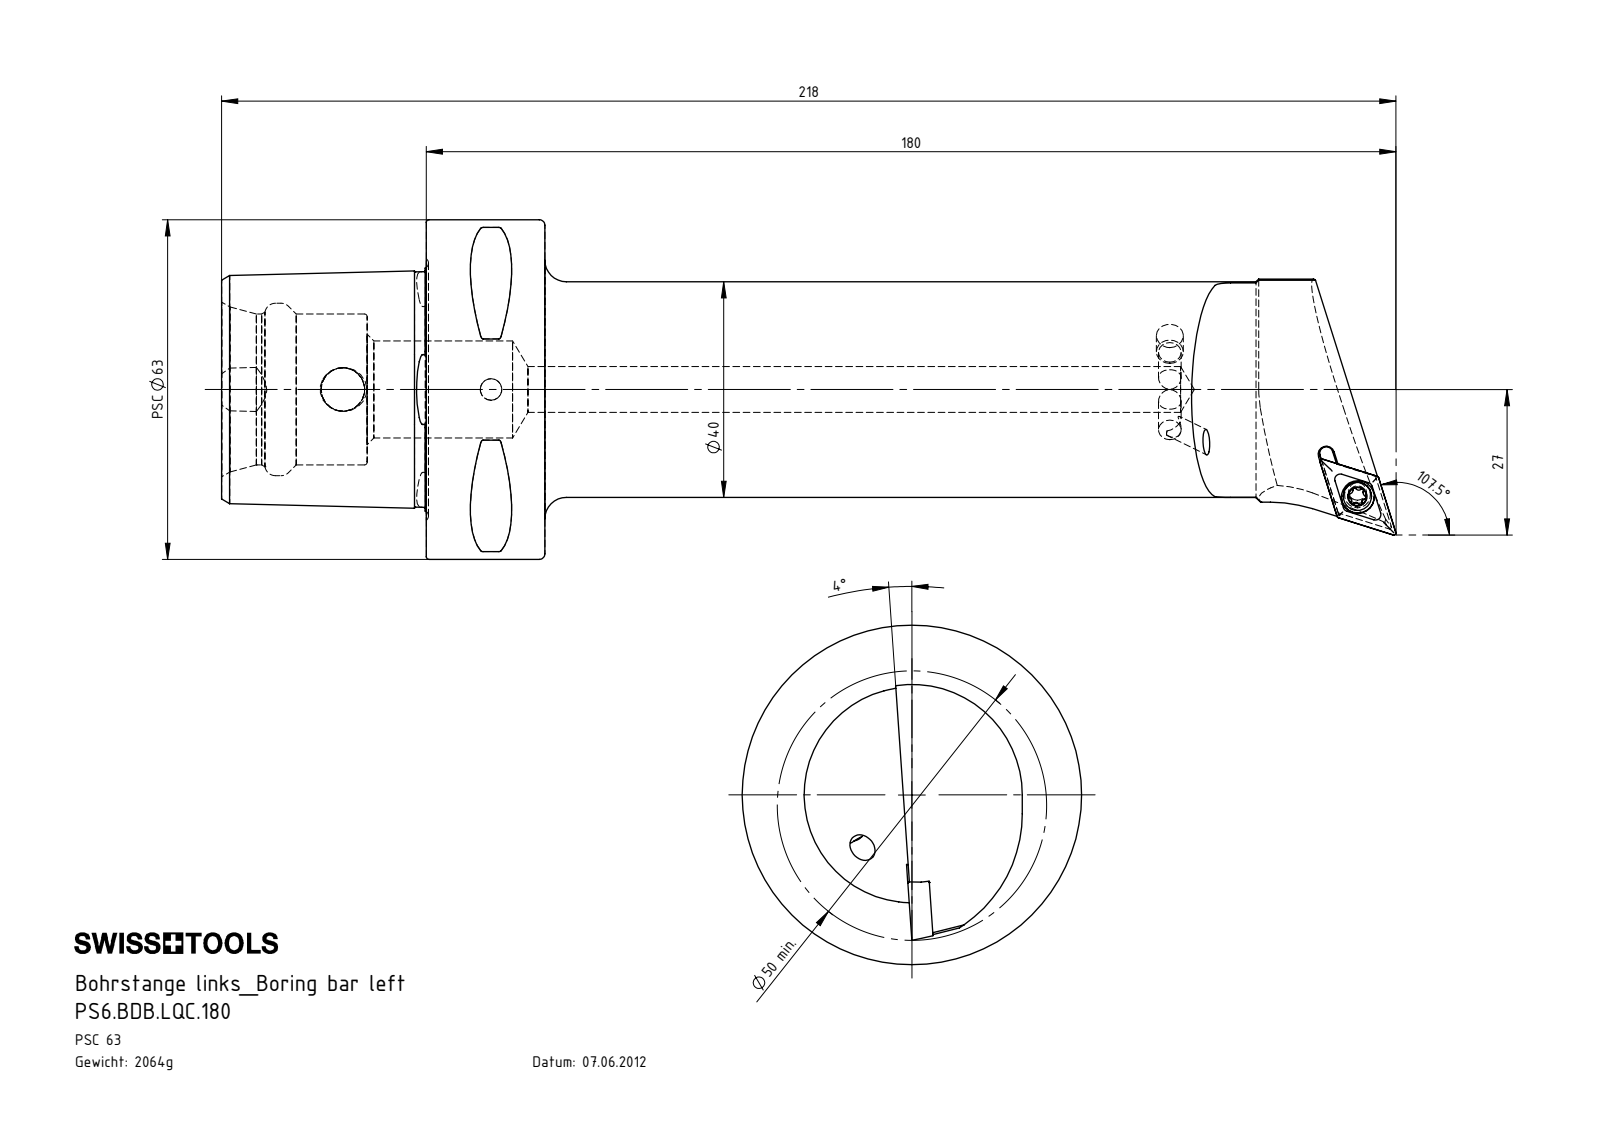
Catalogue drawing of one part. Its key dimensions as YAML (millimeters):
part_name: "PS6-BDB.LQC.180; KVT_MB_600_050; WCB-ER2.001.009_A; DCMT11T304 (+1 more)"
step_written_by: "SolidWorks 2012 (CONFIG_CONTROL_DESIGN)"
units: millimeters
bodies: {solids: 5, faces: 287, planar: 53, cylindrical: 76, other: 158}
overall_size: [218, 63, 63]
volume: 262771
surface_area: 42631
round_holes:
  - {diameter: 4, count: 2}
  - {diameter: 4.2, count: 2}
  - {diameter: 3.3, count: 1}
  - {diameter: 4.4, count: 1}
  - {diameter: 6.1, count: 1}
  - {diameter: 8.1, count: 1}
  - {diameter: 8.5, count: 1}
  - {diameter: 18, count: 1}
  - {diameter: 28, count: 1}
  - {diameter: 32, count: 1}
round_bosses_or_shafts:
  - {diameter: 63, count: 1}
  - {diameter: 40, count: 1}
  - {diameter: 5.25, count: 1}
  - {diameter: 5, count: 1}
  - {diameter: 4, count: 1}
partial_cylinders:
  - {radius: 0.5, count: 8}
  - {radius: 0.34, count: 6}
  - {radius: 0.59, count: 6}
  - {radius: 6, count: 2}
  - {radius: 1.25, count: 1}
  - {radius: 20.5, count: 1}
  - {radius: 25, count: 1}
  - {radius: 26, count: 1}
face_to_face_distances: [22, 38, 60, 24.88, 27, 11, 33, 55.8, 3.67, 37.8]
hole_center_spacings: [27.5]
